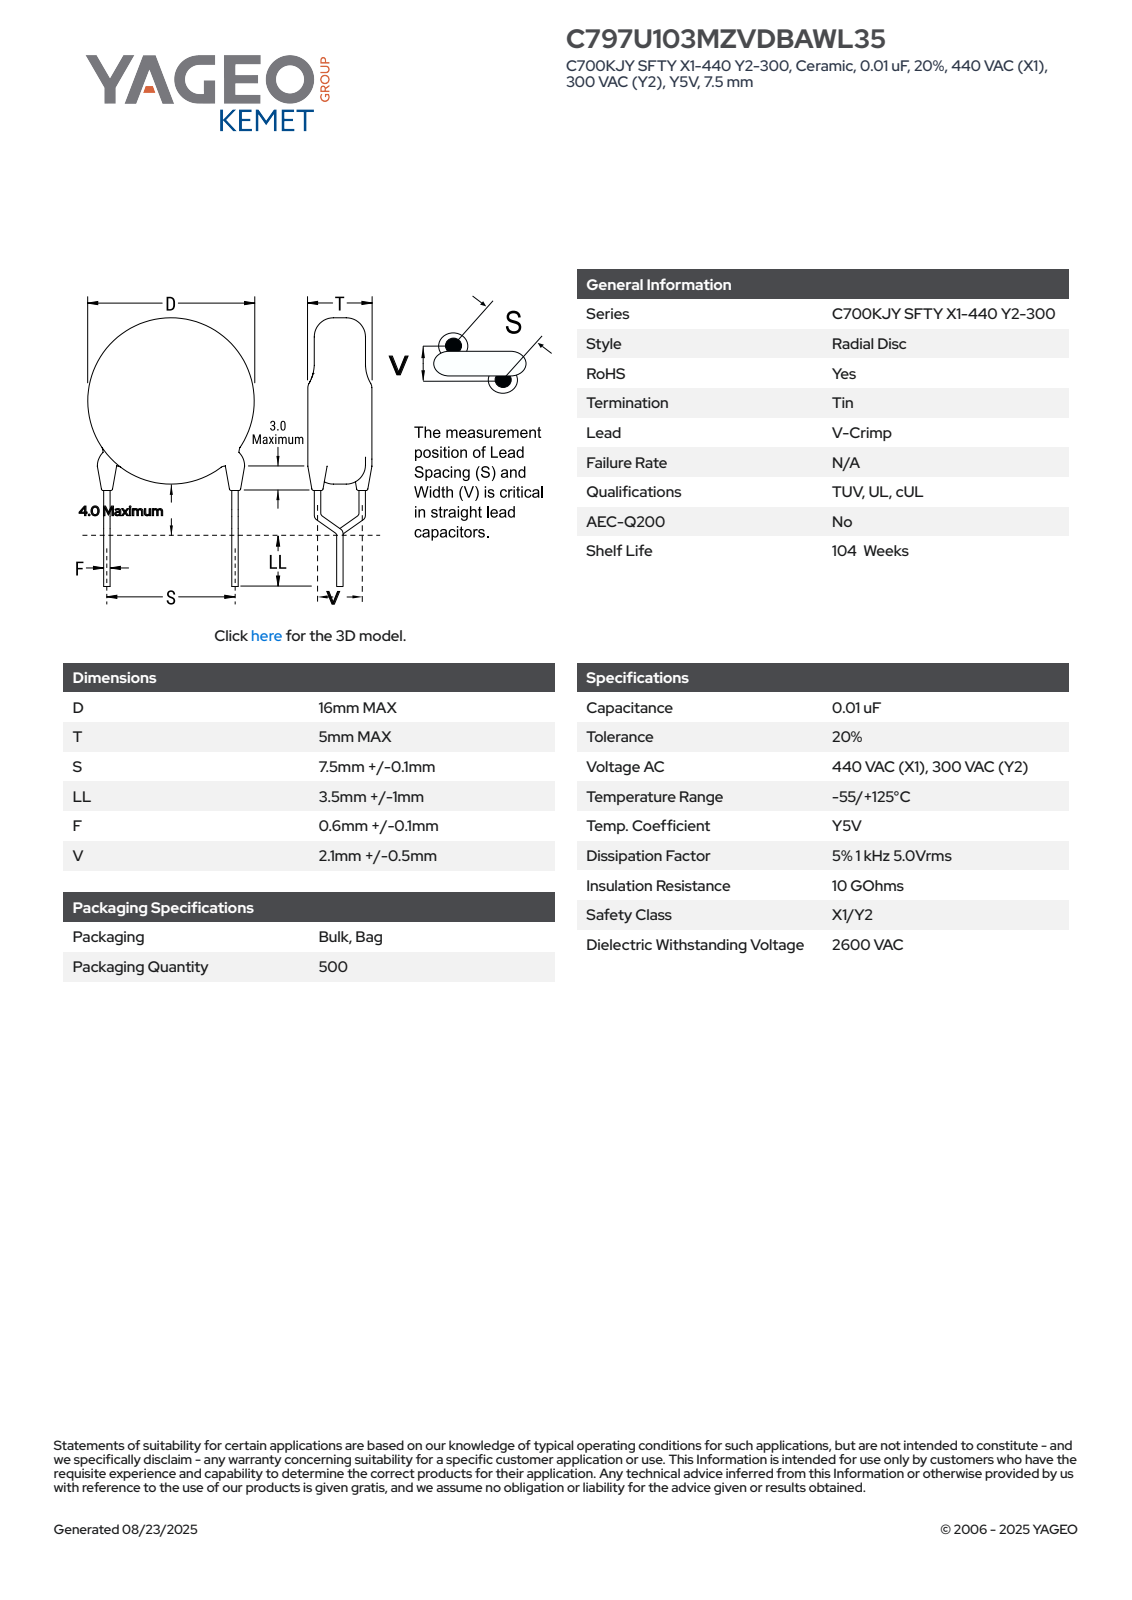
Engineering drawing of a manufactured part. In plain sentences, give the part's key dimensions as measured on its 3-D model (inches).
The part is named "CCD_VC16X5_D16T5S7.5LL4.5F0.7V2.1". Its 3-D file was written by "SolidWorks 2021 (AUTOMOTIVE_DESIGN)". It is 4 solids with 85 faces: 63 planar, 18 cylindrical and 4 other. Overall it measures 0.807 by 0.63 by 0.197 inches. Its volume is 0.06 cubic inches and its surface area 1.02 square inches. Round bosses or shafts: 6 of diameter 0.028, 2 of diameter 0.047, 1 of diameter 0.63. The main face-to-face distances are 0.197, 0.177, 0.542, 0.365, 0.466, 0.289, 0.076, 0.021, 0.014, 0.312.
